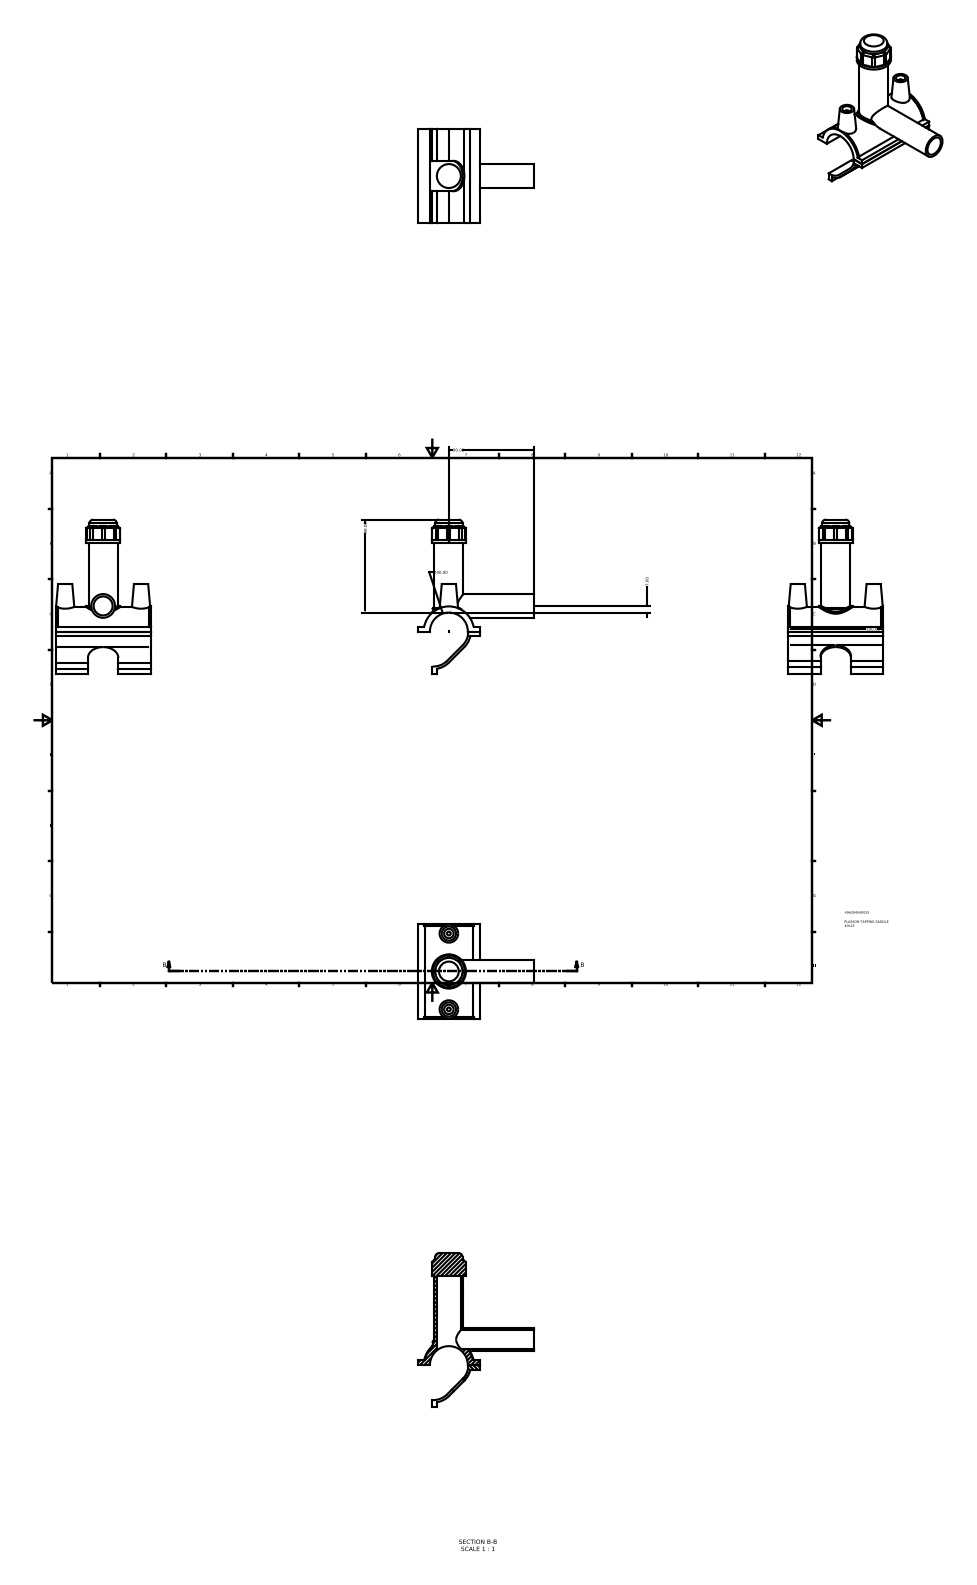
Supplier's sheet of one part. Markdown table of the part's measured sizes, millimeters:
| quantity | value |
| --- | --- |
| part name | 496304040025 |
| STEP written by | Autodesk Inventor 2015 (AUTOMOTIVE_DESIGN) |
| units | millimeters |
| bodies | 2 solids, 115 faces (68 planar, 32 cylindrical, 15 other) |
| overall size | 162.4 × 122.5 × 100 |
| volume | 124 327 mm³ |
| surface area | 61 818 mm² |
| round holes (diameter × count) | 10 × 2, 20 × 1, 25.2 × 1 |
| round bosses / shafts (diameter × count) | 4 × 2, 36 × 1, 30.6 × 1, 28.8 × 1, 25 × 1 |
| partial cylindrical surfaces (radius × count) | 4 × 8, 20.52 × 2, 23.12 × 2, 16 × 1, 17.1 × 1, 20 × 1, 26 × 1, 26.52 × 1 |
| main face-to-face distances | 4.95, 2.6, 9.9, 98.4, 93.45, 88.5, 100, 49.9, 15.1, 65 |
| hole center spacings | 40, 80 |
